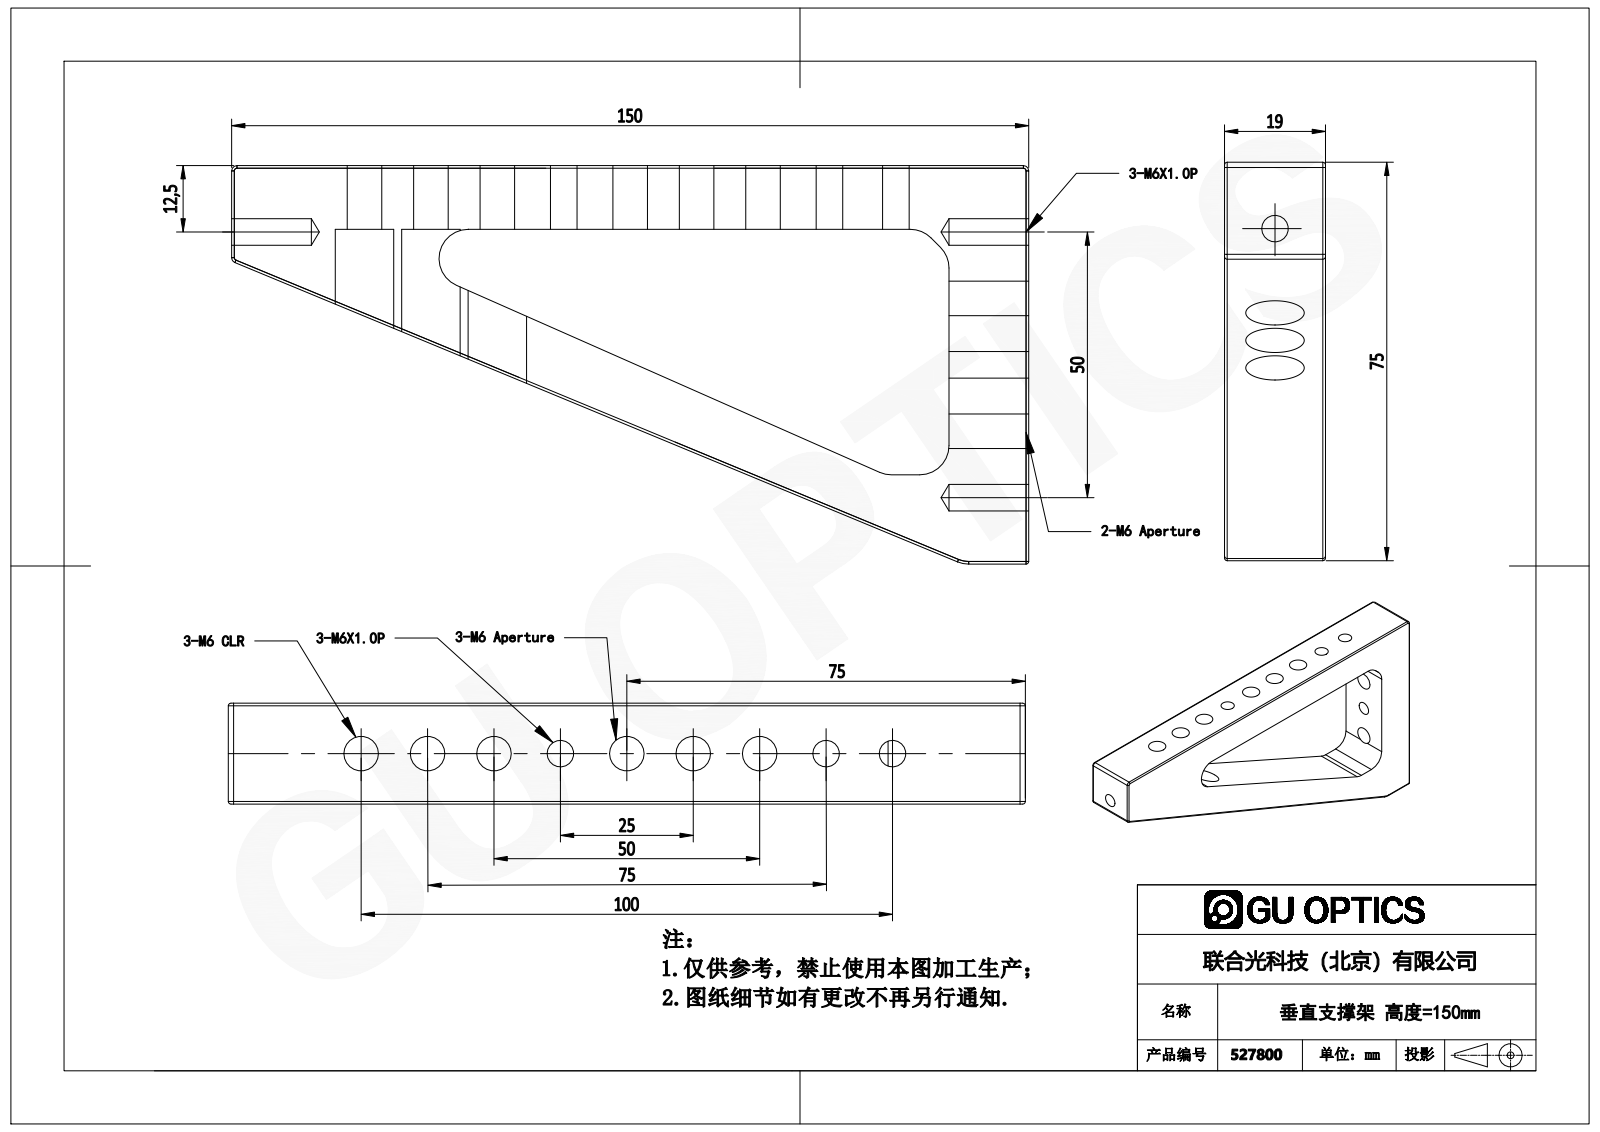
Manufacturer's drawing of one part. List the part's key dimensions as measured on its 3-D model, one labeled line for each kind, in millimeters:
Part name (STEP PRODUCT): VAB-150
STEP written by: SolidWorks 2012 (CONFIG_CONTROL_DESIGN)
Units: millimetres
Bodies: 1 solid, 65 faces (14 planar, 38 cylindrical, 13 other)
Overall size (bounding box): 150 × 75 × 19
Volume: 75 146 mm³ · Surface area: 25 301 mm²
Round holes (diameter × count): ⌀6.5 ×8, ⌀5 ×6, ⌀11 ×3
Partial cylindrical surfaces — rounded edges, fillets, slot ends (radius × count): R0.5 ×11, R5.5 ×6, R1 ×3
Main face-to-face distances: 19, 12, 15, 135, 150, 63, 75, 16.8, 46.2, 58.2
Hole centre spacings: 12.5, 25, 37.5, 50, 62.5, 75, 87.5, 100
